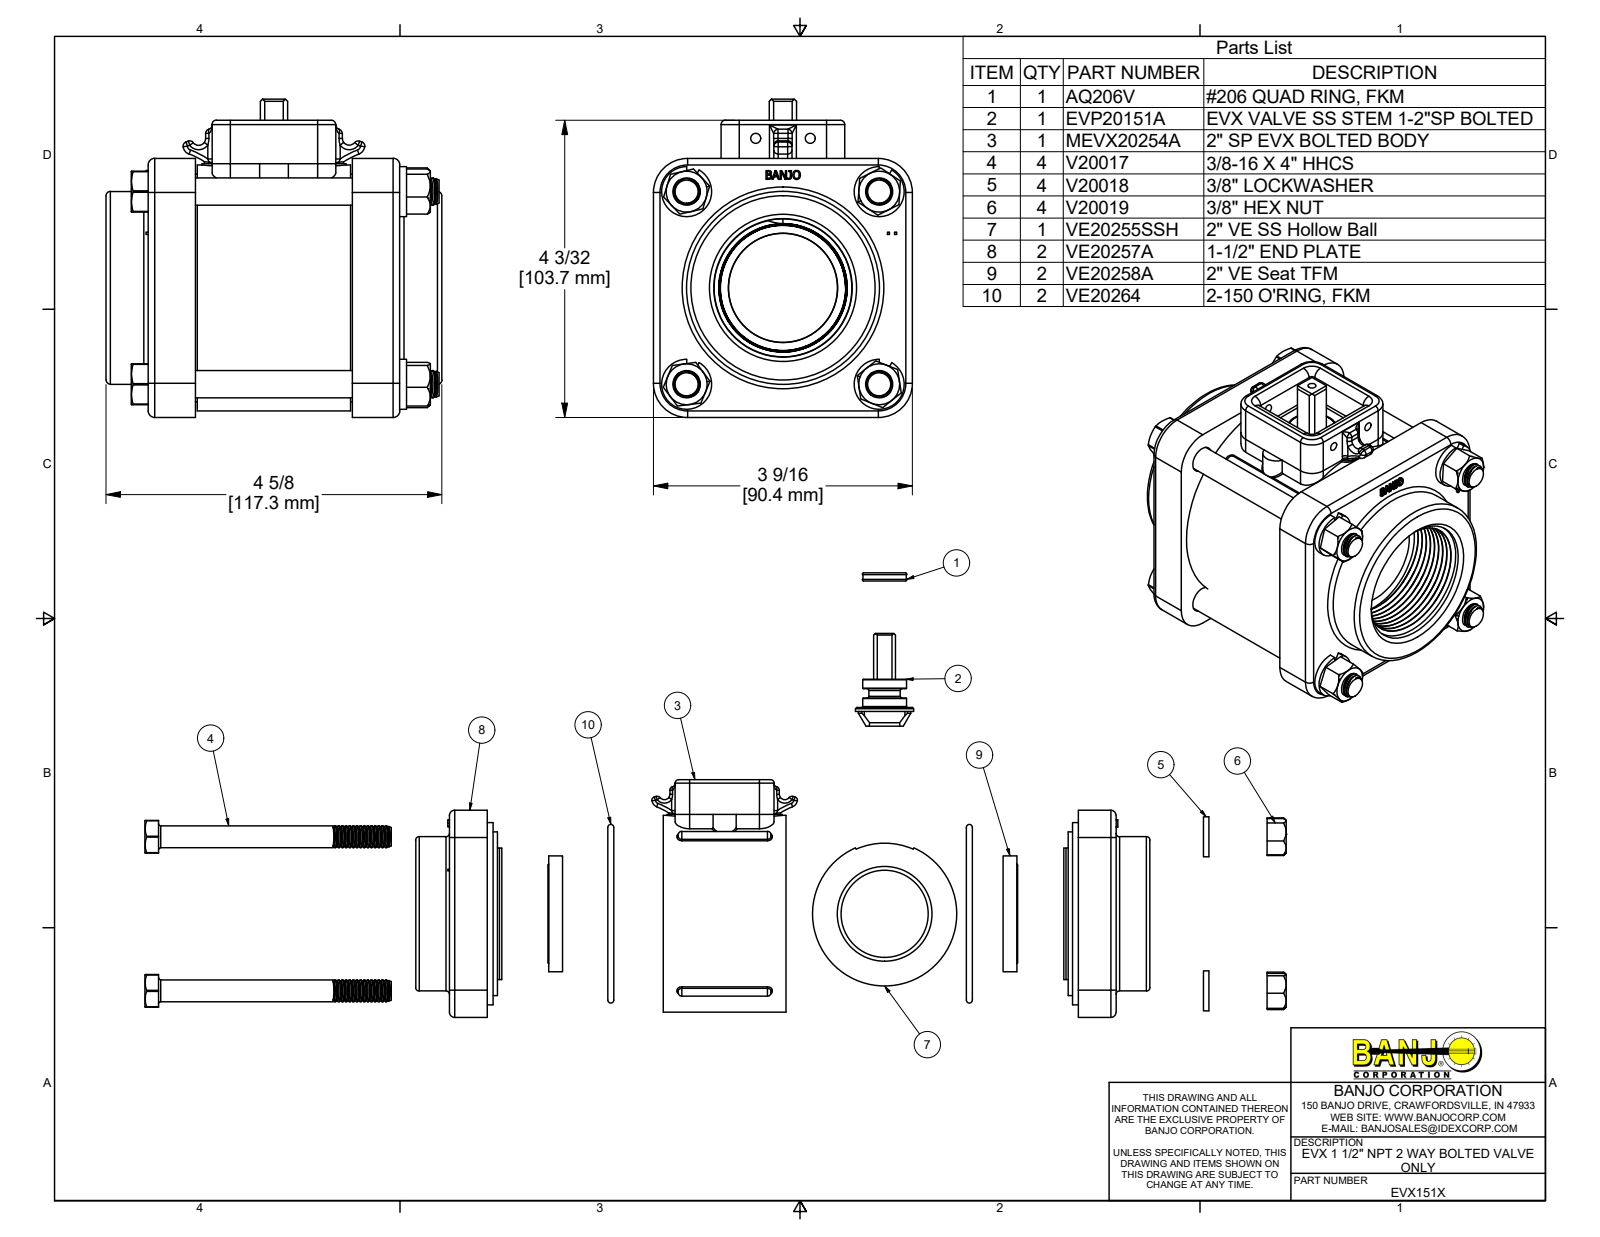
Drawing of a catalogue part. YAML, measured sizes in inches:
part_name: "EVX151X; MEVX20254A; MEVX20254AX; V20017 (+8 more)"
step_written_by: "Autodesk Inventor 2019 (AUTOMOTIVE_DESIGN)"
units: inches
bodies: {solids: 22, faces: 1263, planar: 338, cylindrical: 382, other: 543}
overall_size: [4.618, 4.373, 3.56]
volume: 30.28
surface_area: 247.3
round_holes:
  - {diameter: 0.307, count: 4}
  - {diameter: 0.385, count: 4}
  - {diameter: 0.406, count: 4}
  - {diameter: 0.135, count: 2}
  - {diameter: 1.5, count: 2}
  - {diameter: 0.76, count: 1}
  - {diameter: 1.02, count: 1}
  - {diameter: 1.495, count: 1}
  - {diameter: 1.995, count: 1}
  - {diameter: 2.56, count: 1}
  - {diameter: 3.063, count: 1}
  - {diameter: 3.14, count: 1}
round_bosses_or_shafts:
  - {diameter: 0.324, count: 60}
  - {diameter: 0.687, count: 4}
  - {diameter: 0.375, count: 4}
  - {diameter: 3.38, count: 1}
  - {diameter: 3.13, count: 1}
  - {diameter: 2.812, count: 1}
  - {diameter: 2.65, count: 1}
  - {diameter: 2.26, count: 1}
partial_cylinders:
  - {radius: 0.06, count: 28}
  - {radius: 0.09, count: 12}
  - {radius: 0.02, count: 8}
  - {radius: 0.162, count: 8}
  - {radius: 0.125, count: 6}
  - {radius: 0.015, count: 4}
  - {radius: 0.03, count: 4}
  - {radius: 0.21, count: 4}
face_to_face_distances: [0.65, 2.808, 0.825, 2.633, 0.175, 1.983, 3.56, 1.883, 3.458, 2.158]
hole_center_spacings: [1.872, 2.648, 1.198, 1.849, 2.088, 3.509, 3.745, 3.781]
